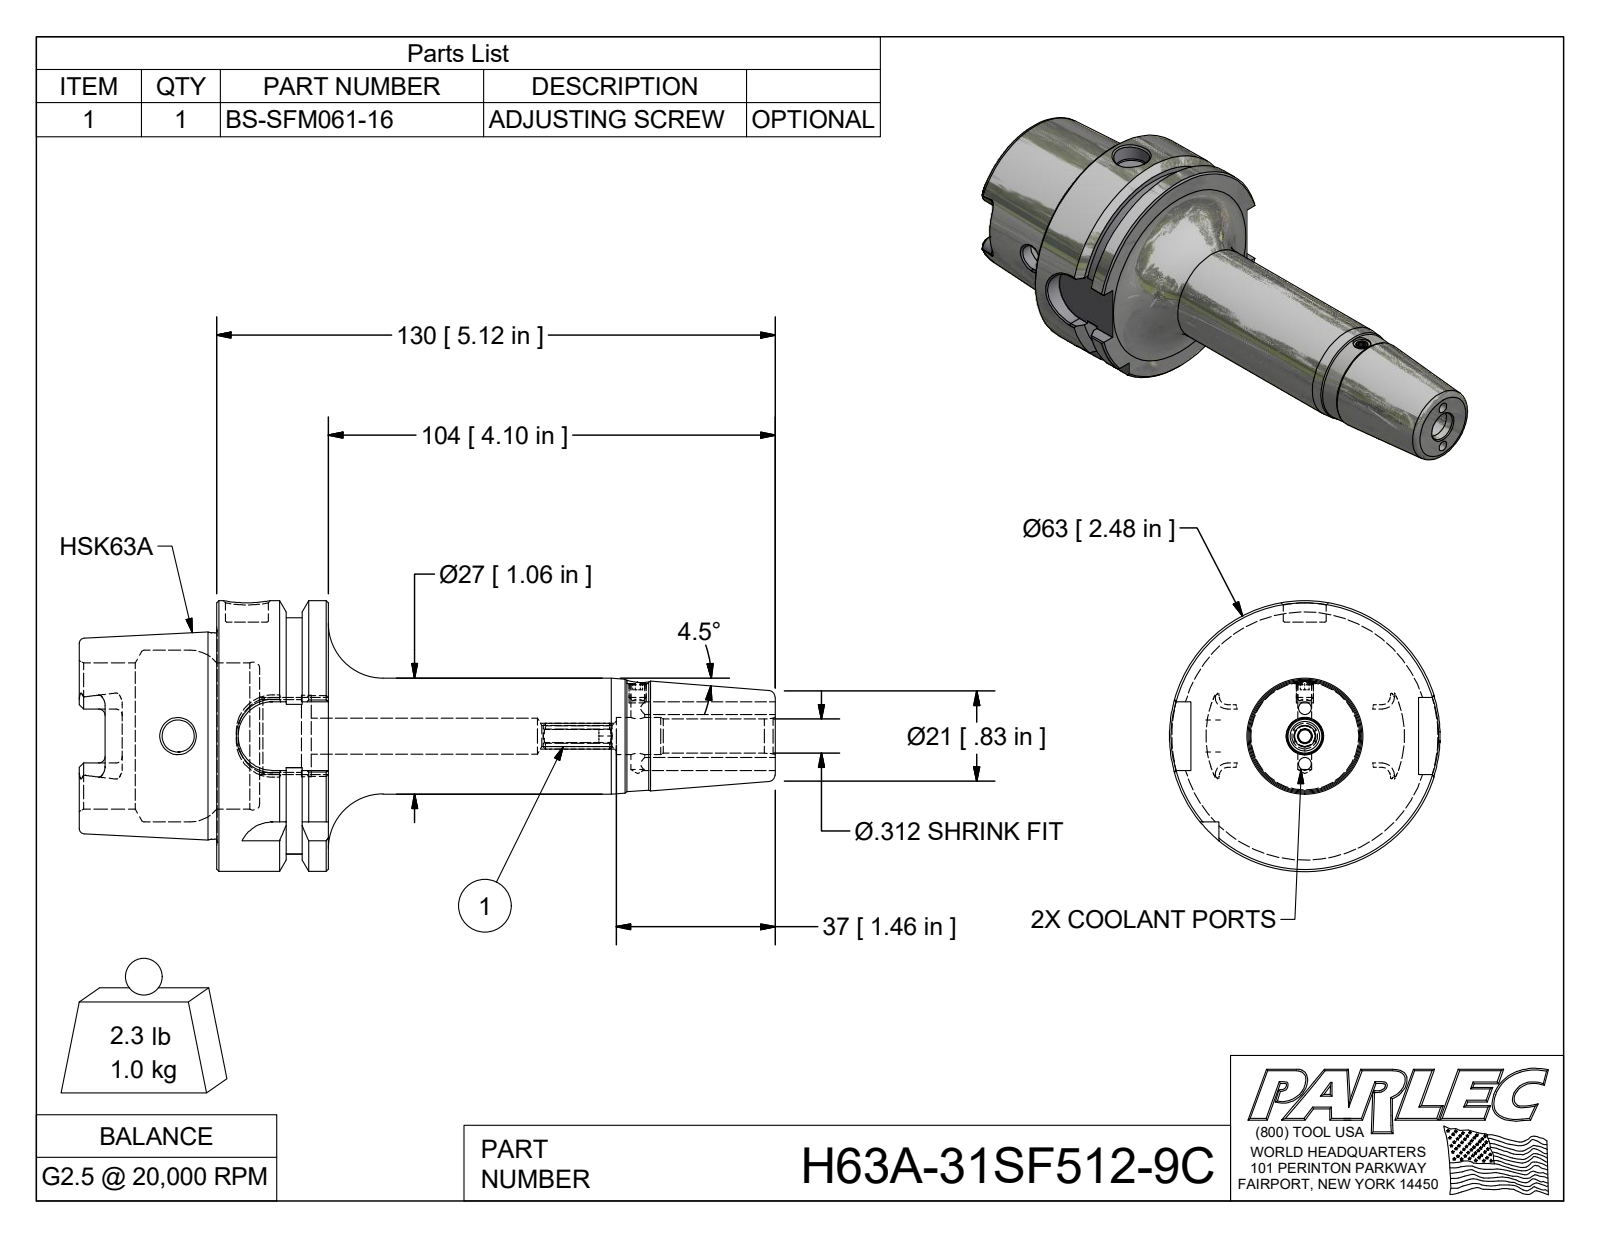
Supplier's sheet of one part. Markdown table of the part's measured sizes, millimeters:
| quantity | value |
| --- | --- |
| part name | H63A-31SF512-9C |
| STEP written by | Autodesk Inventor 2018 (AUTOMOTIVE_DESIGN) |
| units | millimeters |
| bodies | 1 solid, 152 faces (53 planar, 42 cylindrical, 57 other) |
| overall size | 162 × 63 × 63 |
| volume | 134 042 mm³ |
| surface area | 33 527 mm² |
| round holes (diameter × count) | 3 × 2, 3.25 × 1, 4.92 × 1, 5 × 1, 7.5 × 1, 7.92 × 1, 8.4 × 1, 8.68 × 1, 10 × 1, 16.92 × 1, 19.02 × 1, 34 × 1 |
| round bosses / shafts (diameter × count) | 63 × 1, 48.04 × 1, 27 × 1 |
| partial cylindrical surfaces (radius × count) | 1.5 × 6, 2.88 × 4, 8 × 4, 27.5 × 1 |
| main face-to-face distances | 26, 6.12, 9.88, 10, 16, 32, 42, 58, 51.88, 19.88 |
| hole center spacings | 6.5, 13, 91.02 |
